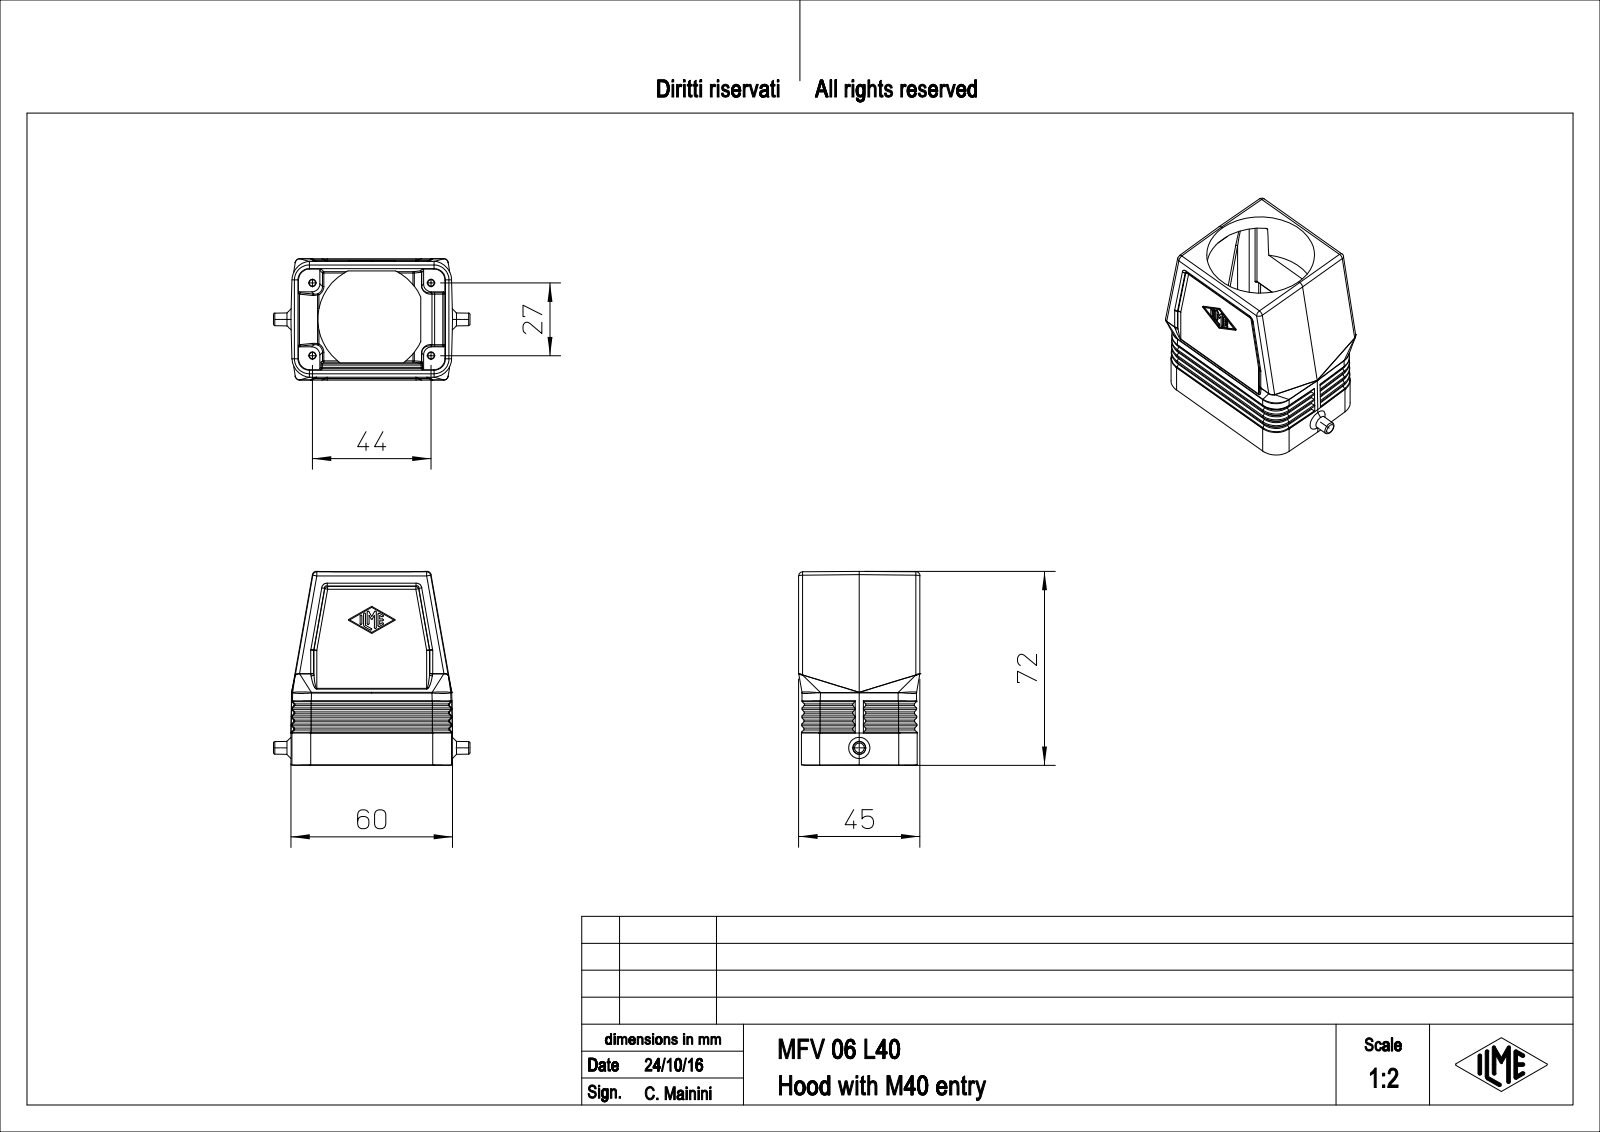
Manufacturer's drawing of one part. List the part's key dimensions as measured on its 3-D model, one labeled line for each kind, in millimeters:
Part name (STEP PRODUCT): MFV_06_L40
STEP written by: PTC Creo Elements/Direct Modeling 19.0E 27-Jun-2016 (C) Parametric Technology GmbH (AUTOMOTIVE_DESIGN)
Units: millimetres
Bodies: 1 solid, 385 faces (159 planar, 102 cylindrical, 124 other)
Overall size (bounding box): 73 × 72 × 45
Volume: 53 313 mm³ · Surface area: 27 902 mm²
Round holes (diameter × count): ⌀2.75 ×4, ⌀40 ×1
Round bosses / shafts (diameter × count): ⌀4.62 ×1
Partial cylindrical surfaces — rounded edges, fillets, slot ends (radius × count): R0.5 ×54, R1.5 ×10, R7 ×8, R3 ×4, R4.2 ×4
Main face-to-face distances: 43, 7.95, 1.85, 2, 1, 44, 8.5, 4, 45, 60
Hole centre spacings: 25.81, 27, 44, 51.62
